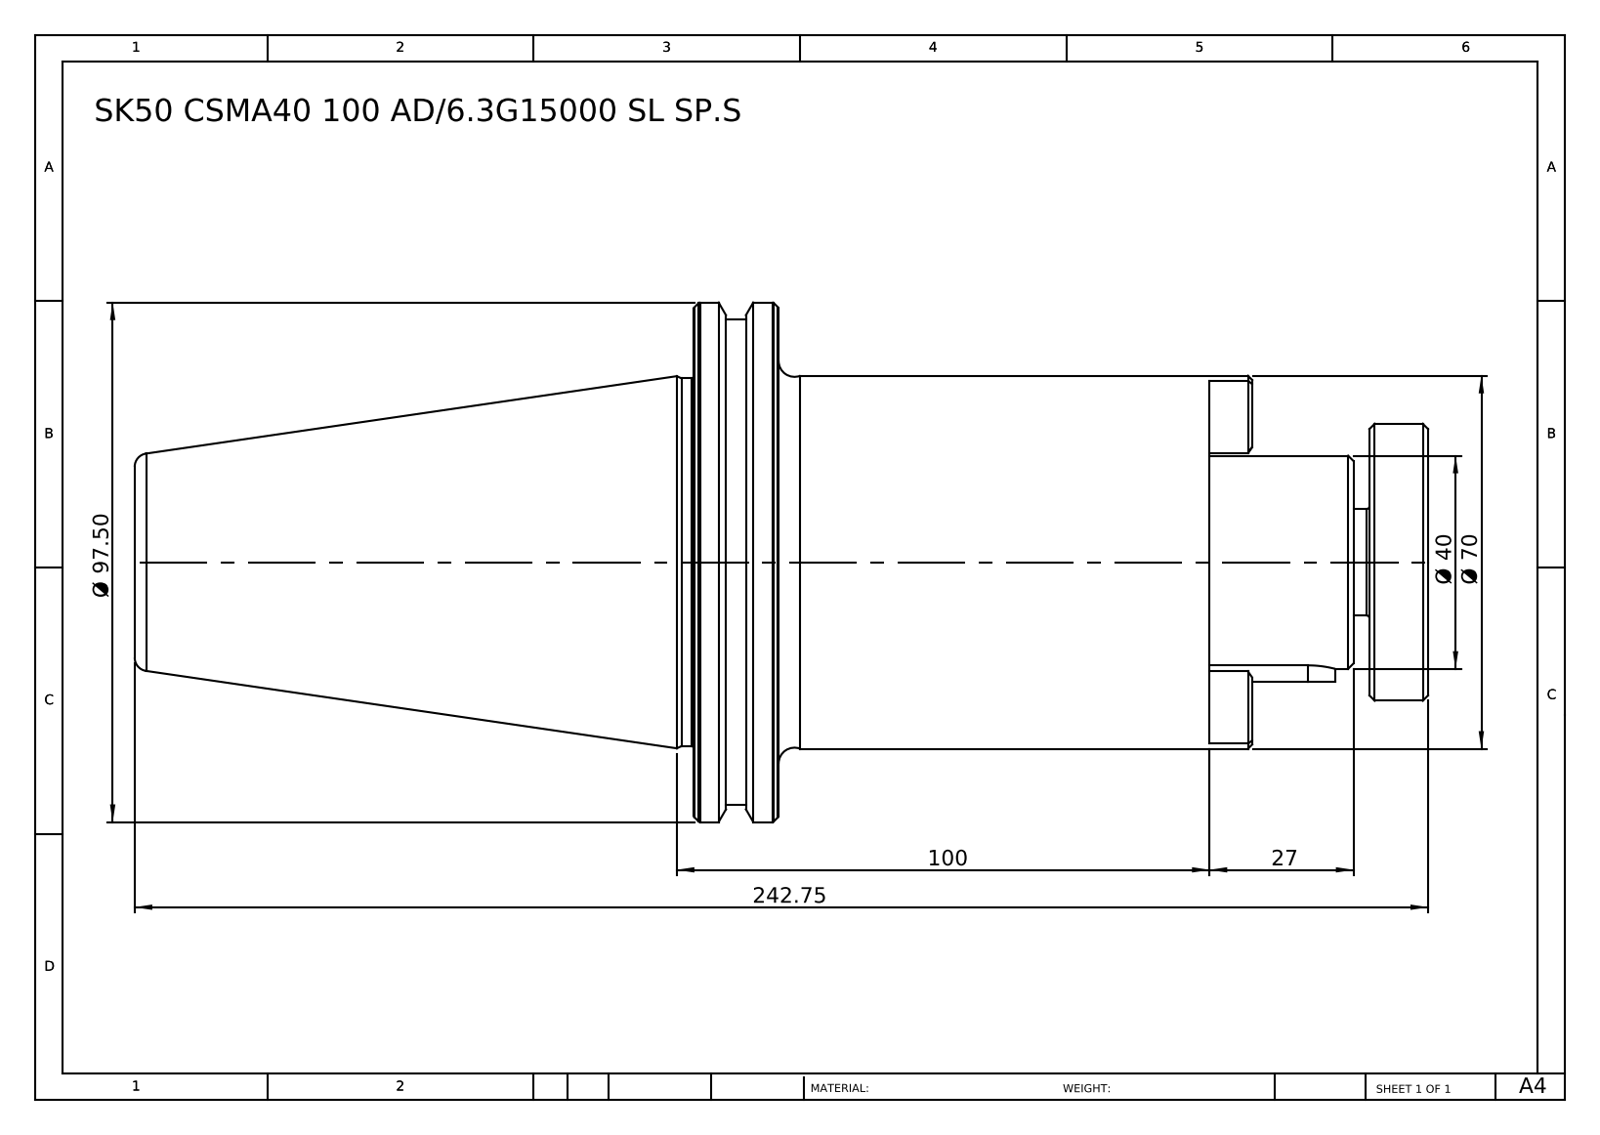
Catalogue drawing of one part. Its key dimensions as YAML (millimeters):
part_name: "SK 50 CSMA40 100 AD-6.3G15000 SL SP"
step_written_by: "SolidWorks 2014 (CONFIG_CONTROL_DESIGN)"
units: millimeters
bodies: {solids: 2, faces: 96, planar: 24, cylindrical: 24, other: 48}
overall_size: [242.75, 97.5, 97.5]
volume: 742282
surface_area: 65349
round_holes:
  - {diameter: 14, count: 1}
  - {diameter: 17, count: 1}
round_bosses_or_shafts:
  - {diameter: 97.5, count: 1}
  - {diameter: 91.25, count: 1}
  - {diameter: 70, count: 1}
  - {diameter: 69, count: 1}
  - {diameter: 52, count: 1}
  - {diameter: 40, count: 1}
  - {diameter: 20, count: 1}
partial_cylinders:
  - {radius: 5, count: 1}
  - {radius: 22, count: 1}
face_to_face_distances: [15.9, 80.9, 96.8, 41, 121.9, 137.8, 11, 30, 110.9, 126.8]
